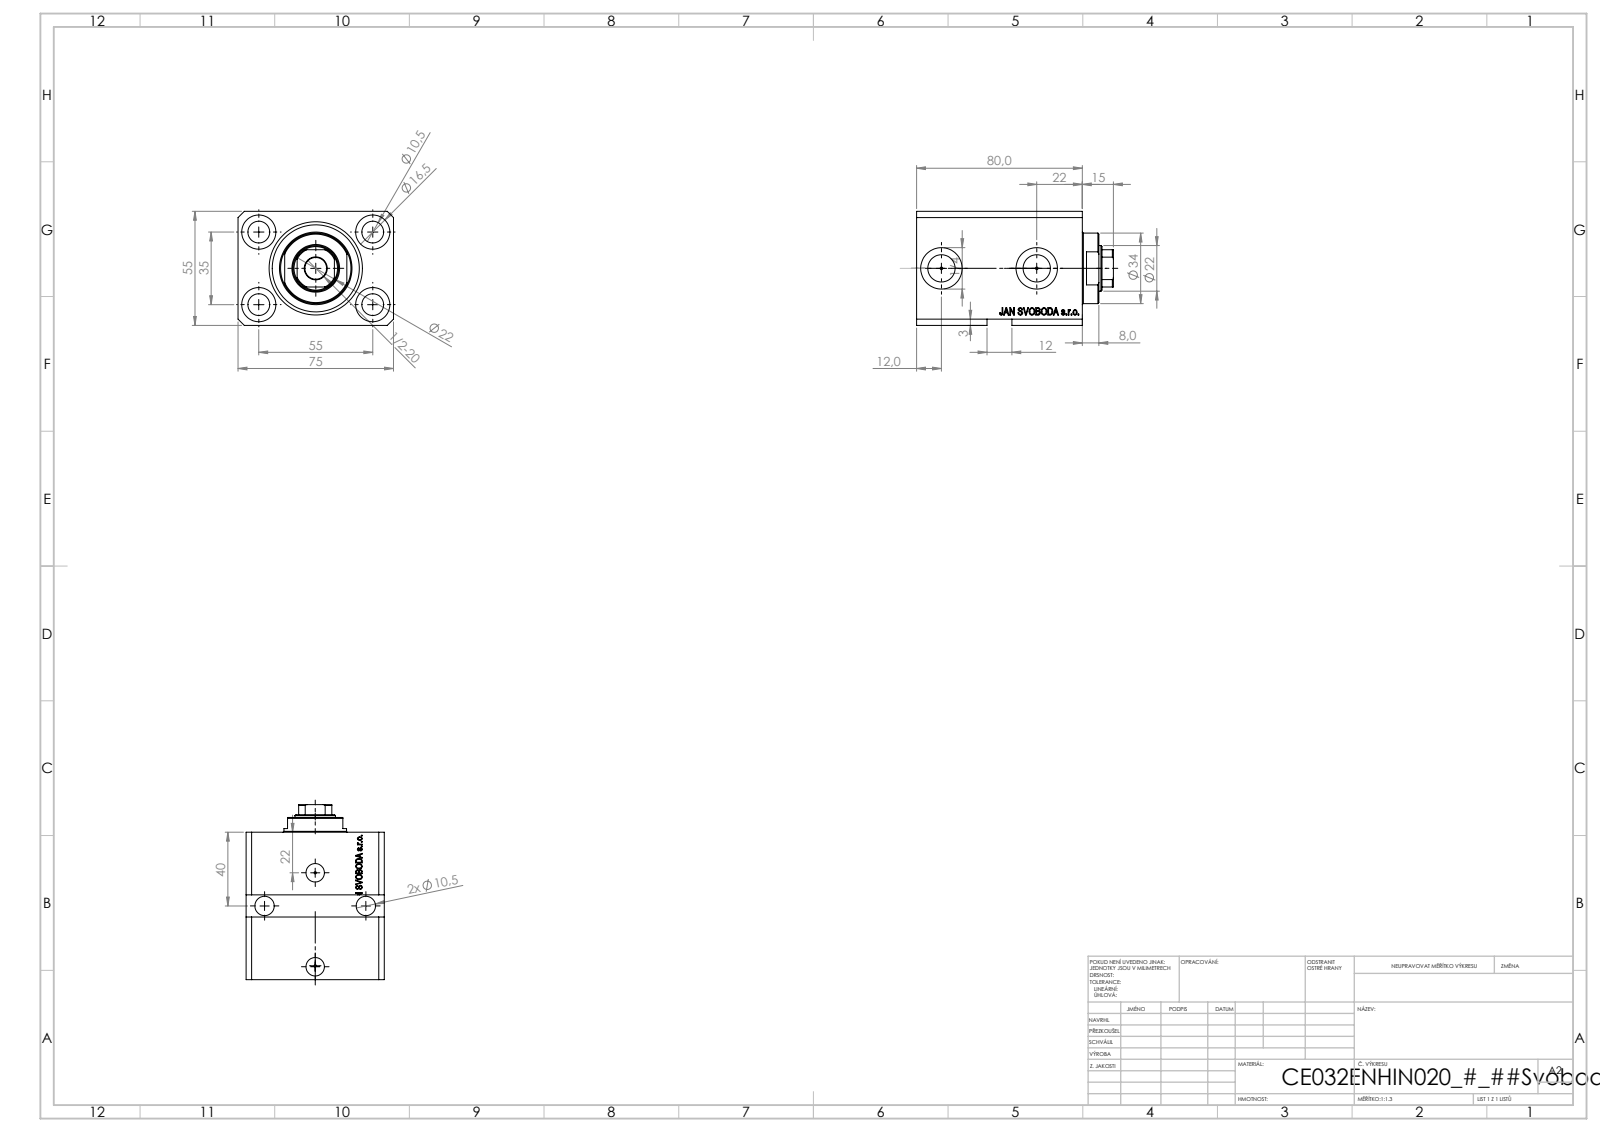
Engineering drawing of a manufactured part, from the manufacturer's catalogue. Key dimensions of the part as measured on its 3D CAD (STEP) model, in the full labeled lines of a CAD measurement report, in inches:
Part name (STEP PRODUCT): V250CE_VC_E; V250CE_C_VCP; V250CE_E_Body
STEP written by: SolidWorks 2019 (CONFIG_CONTROL_DESIGN)
Units: inches
Bodies: 3 solids, 894 faces (438 planar, 84 cylindrical, 372 other)
Overall size (bounding box): 3.74 × 2.953 × 2.165
Volume: 16.81 in³ · Surface area: 104.2 in²
Round holes (diameter × count): ⌀0.413 ×7, ⌀0.049 ×4, ⌀0.65 ×4, ⌀0.394 ×2, ⌀0.518 ×2, ⌀0.787 ×2, ⌀0.866 ×1, ⌀1.26 ×1, ⌀1.772 ×1
Round bosses / shafts (diameter × count): ⌀1.339 ×1
Partial cylindrical surfaces — rounded edges, fillets, slot ends (radius × count): R0.413 ×1
Main face-to-face distances: 2.165, 2.953, 0.591, 3.15, 2.559, 0.39, 2.169, 2.76, 0.433, 2.717
Hole centre spacings: 1.283, 2.165, 1.294, 1.378, 1.675, 1.691, 2.567, 0.021
